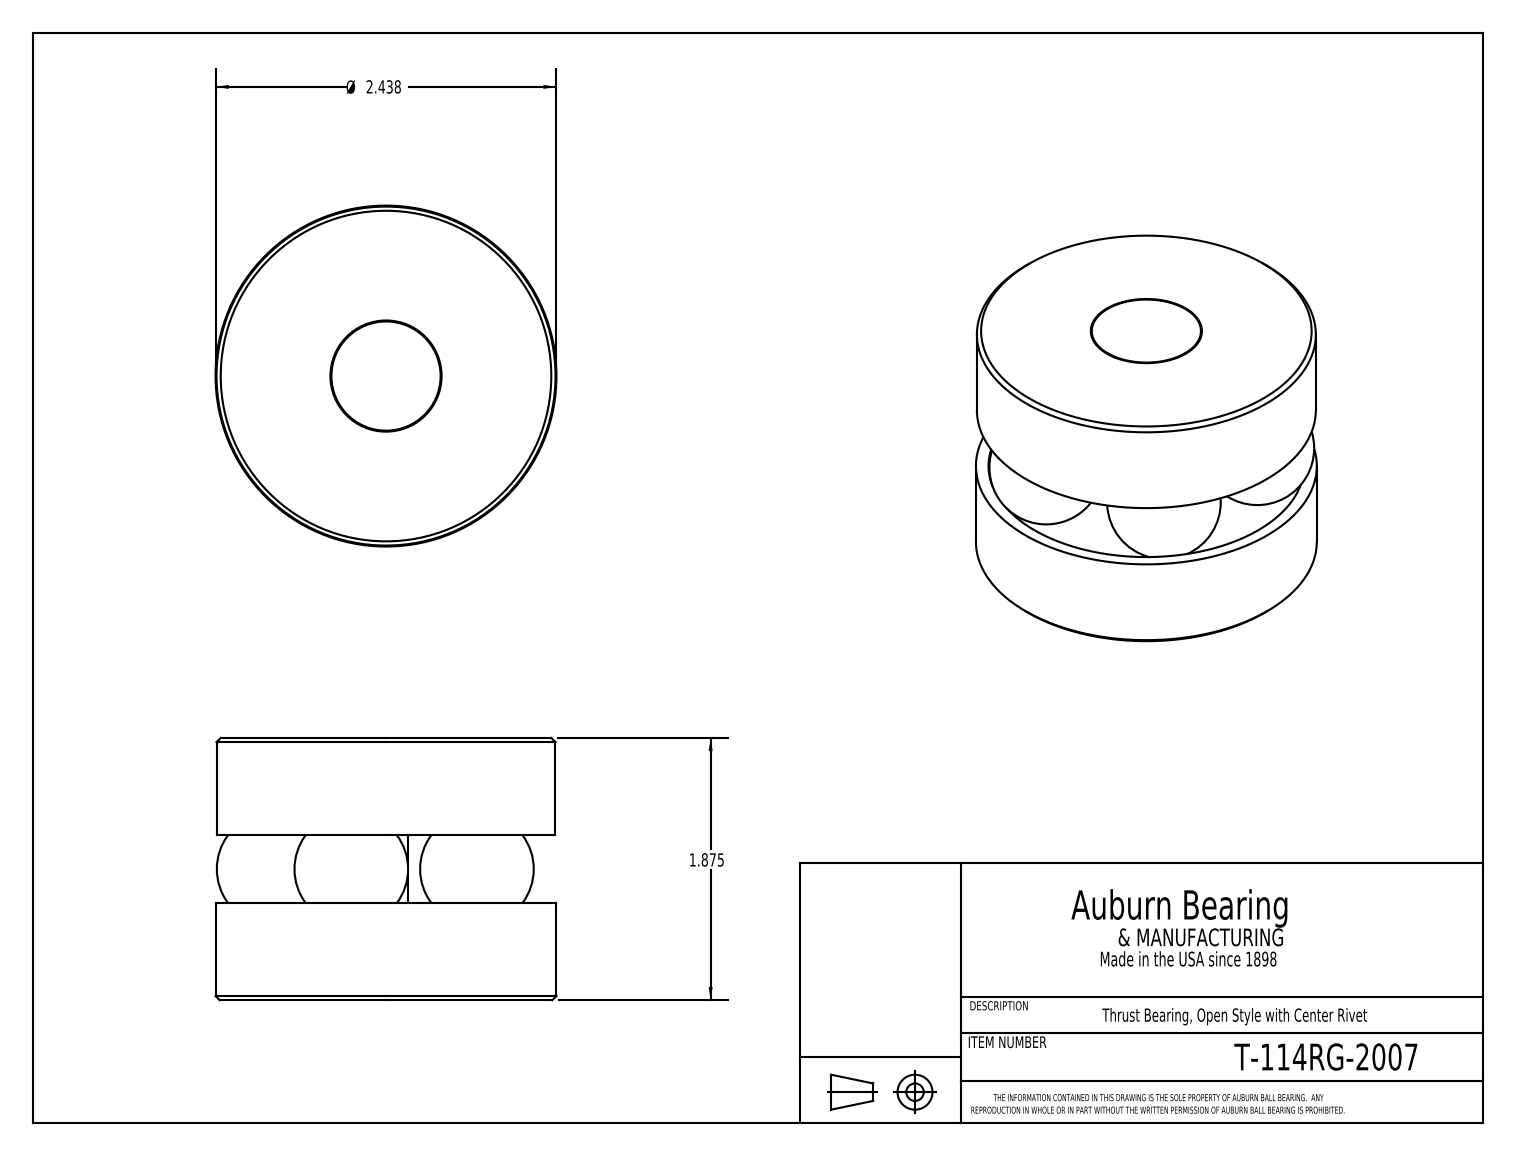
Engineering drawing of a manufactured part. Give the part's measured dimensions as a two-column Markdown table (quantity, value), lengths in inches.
| quantity | value |
| --- | --- |
| part name | T-114RG_T-114RG-2007 |
| STEP written by | SolidWorks 2016 (CONFIG_CONTROL_DESIGN) |
| units | inches |
| bodies | 8 solids, 26 faces (8 planar, 5 cylindrical, 13 other) |
| overall size | 2.438 × 2.438 × 1.875 |
| volume | 7.116 in³ |
| surface area | 44.71 in² |
| round holes (diameter × count) | 0.322 × 1 |
| round bosses / shafts (diameter × count) | 2.437 × 1, 2.423 × 1, 0.312 × 1 |
| main face-to-face distances | 1.875, 0.694, 1.181, 0.487 |
